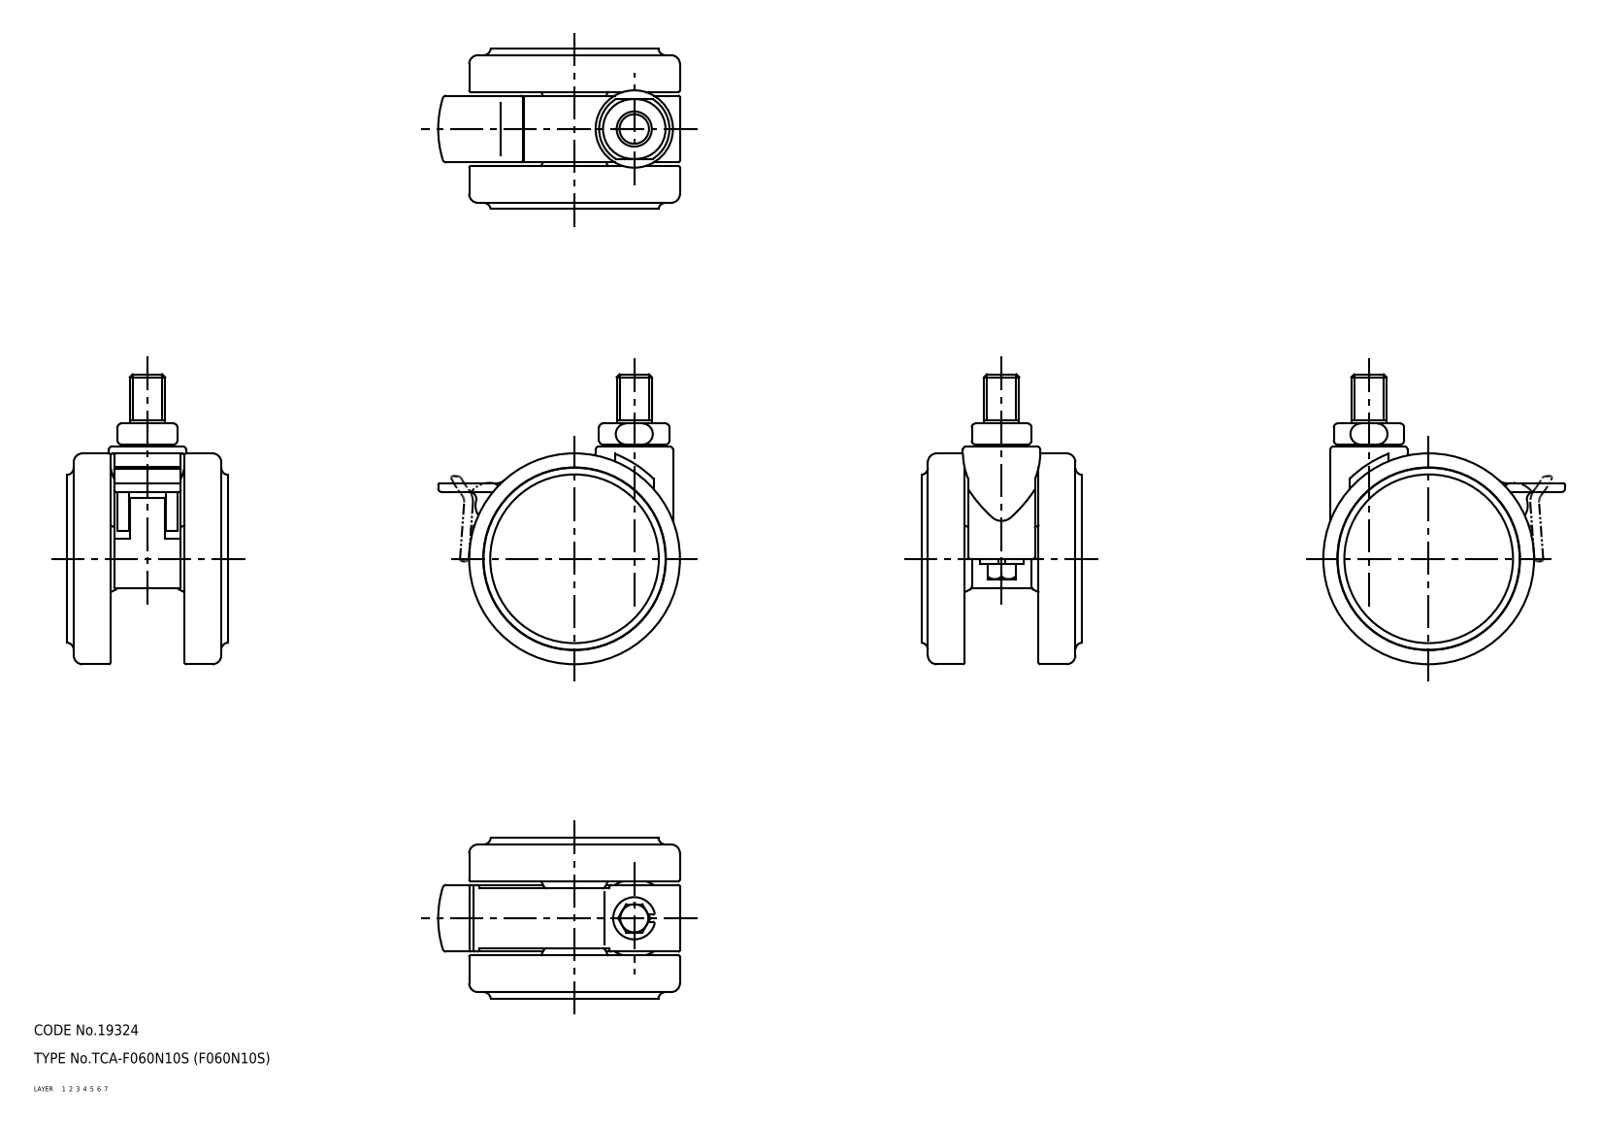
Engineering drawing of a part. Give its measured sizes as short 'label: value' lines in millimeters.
name: 67124951; 67124964; 67124977; 67124990 (+1 more)
written by: CADfix (AUTOMOTIVE_DESIGN)
unit: mm
bodies: 5 solids, 278 faces (0 planar, 0 cylindrical, 278 other)
size: 82.5 × 68.82 × 45.6
volume: 82 795 mm³; area: 29 587 mm²
